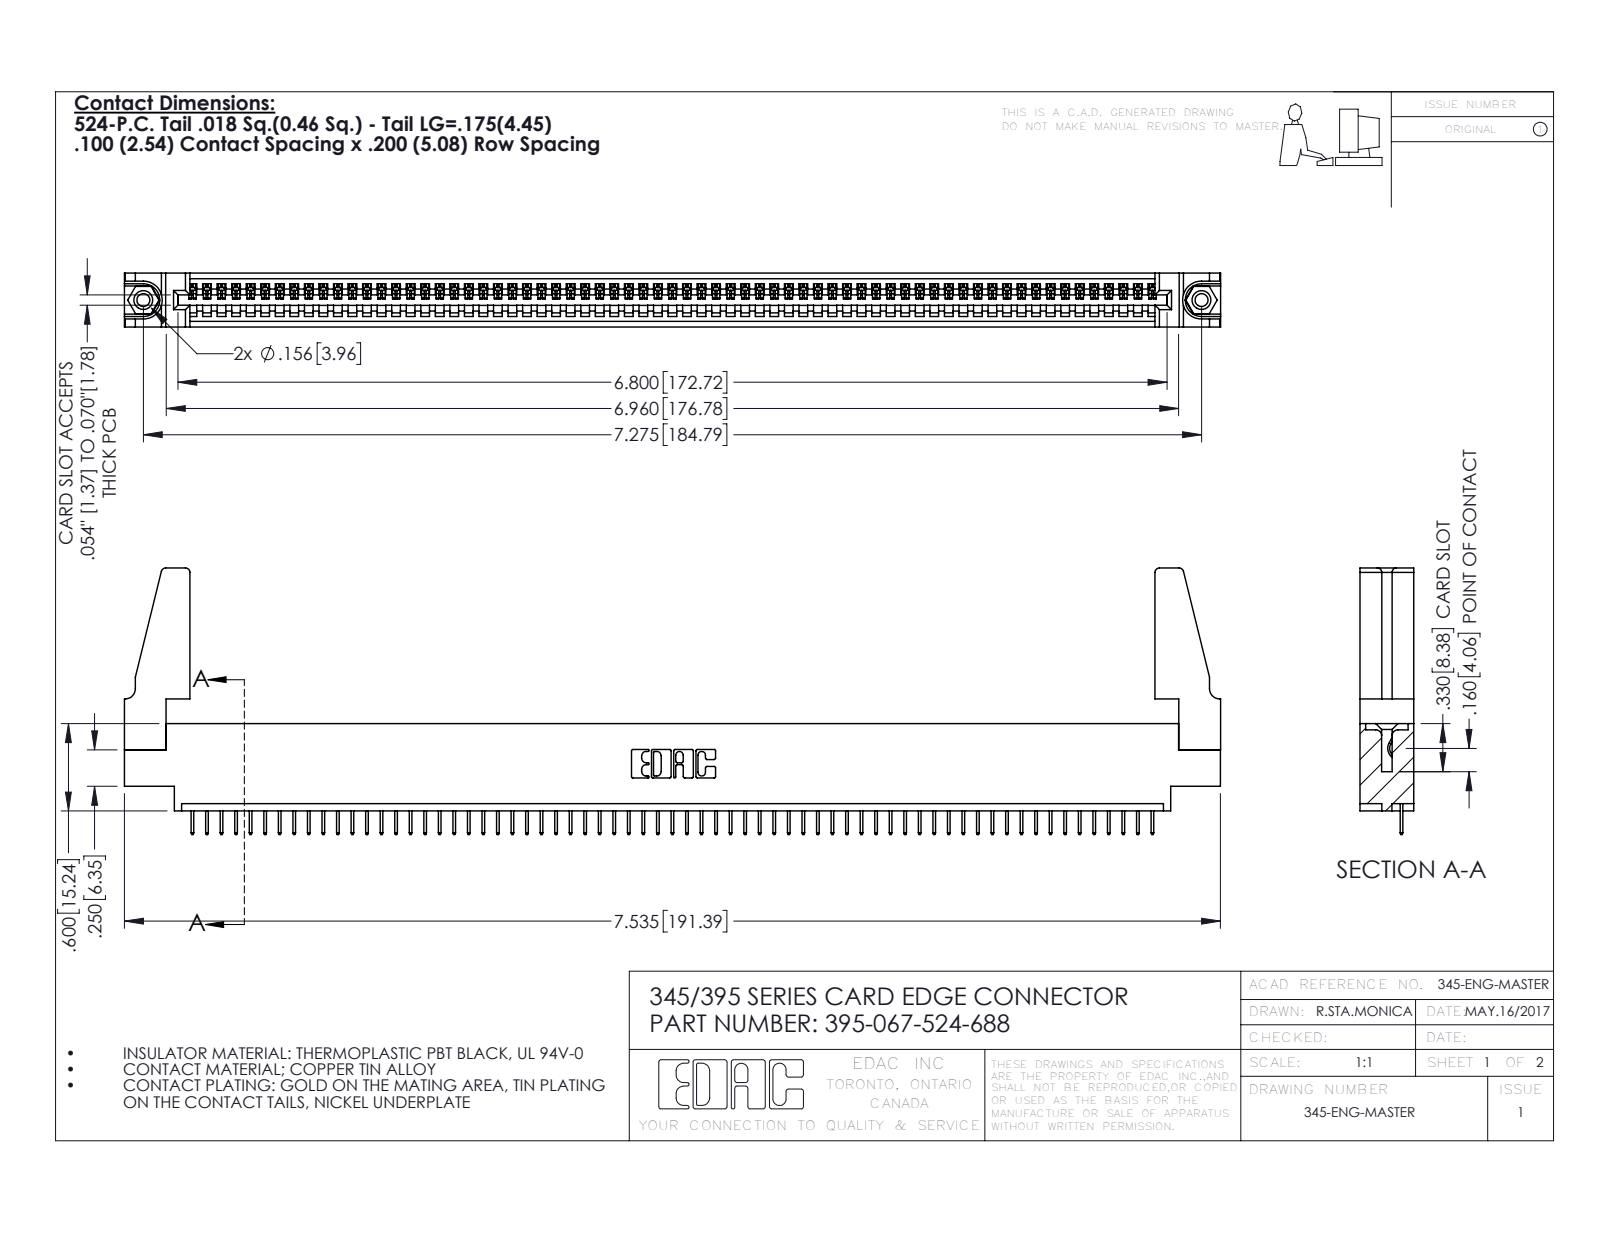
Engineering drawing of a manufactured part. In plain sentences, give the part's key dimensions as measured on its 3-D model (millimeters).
The part is named "345-220-078_345-220-088; 345-250-001_345-250-001-102; 345-292-001_345-293-124; 345 Part_0.170 Offset - 0.156 Dia-TH (+1 more)". Its 3-D file was written by "SolidWorks 2016 (CONFIG_CONTROL_DESIGN)". It is 72 solids with 4408 faces: 3238 planar, 1154 cylindrical and 16 other. Overall it measures 191.4 by 46.5 by 9.4 millimeters. Its volume is 21 250 cubic millimeters and its surface area 26 680 square millimeters. Round holes: 2 of diameter 2.3, 2 of diameter 3.2, 2 of diameter 4, 1 of diameter 1.6. Round bosses or shafts: 2 of diameter 3.9. Partial cylindrical surfaces (rounded edges, fillets, slot ends): 134 of radius 0.2, 22 of radius 0.3, 8 of radius 0.8, 6 of radius 0.2, 6 of radius 0.8, 3 of radius 0.7, 2 of radius 0.8, 2 of radius 1. The main face-to-face distances are 1.8, 7.6, 9.4, 2.5, 6.9, 0.6, 5.1, 5.7, 1.8, 4.4. The hole center spacings are 6.9, 178.8, 184.8.
